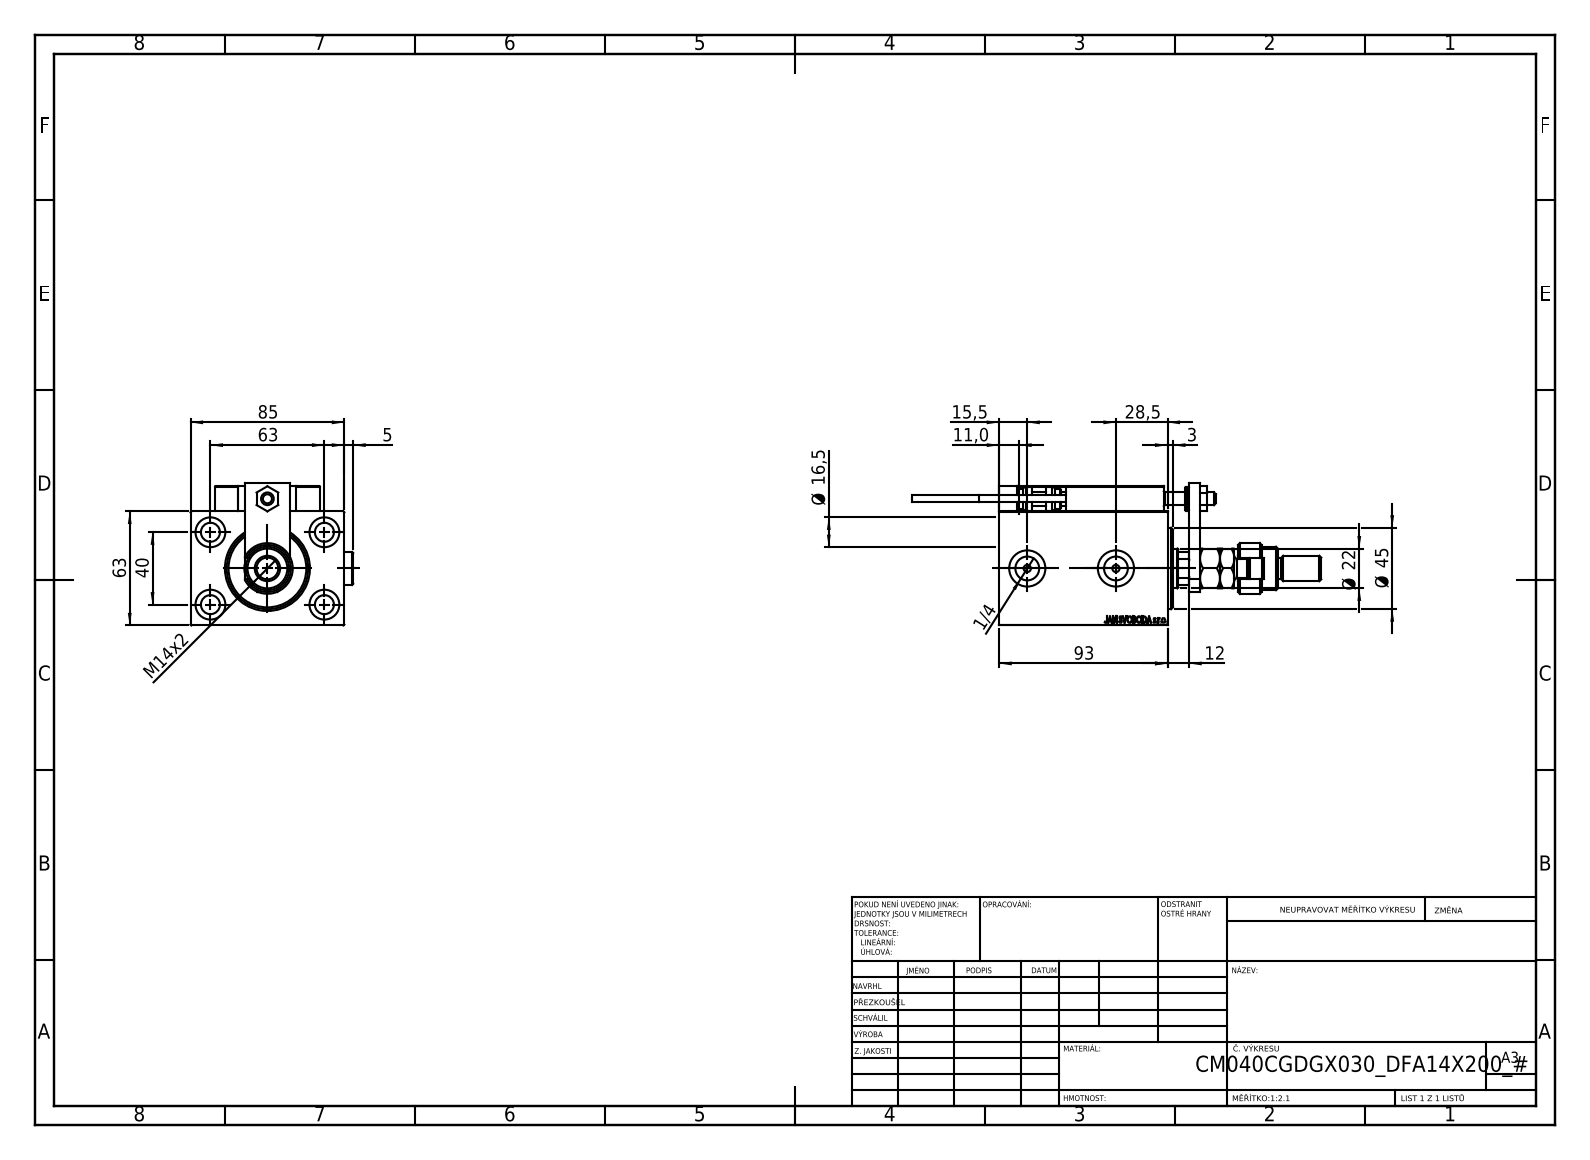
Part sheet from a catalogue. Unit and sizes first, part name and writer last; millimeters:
Units: millimetres
Overall size (bounding box): 226 × 89.9 × 78.5
Round holes (diameter × count): ⌀4 ×6, ⌀8 ×5, ⌀16.5 ×5, ⌀3.2 ×4, ⌀10.5 ×4, ⌀5 ×2, ⌀13.16 ×2, ⌀20 ×2, ⌀7 ×1, ⌀12.5 ×1, ⌀22 ×1, ⌀25.5 ×1
Round bosses / shafts (diameter × count): ⌀18 ×3, ⌀11 ×2, ⌀5 ×2, ⌀3.8 ×2, ⌀28 ×1, ⌀24 ×1, ⌀14 ×1, ⌀13 ×1
Partial cylindrical surfaces — rounded edges, fillets, slot ends (radius × count): R0.3 ×30, R3 ×2, R9.75 ×1, R10.5 ×1
Main face-to-face distances: 63, 12, 85, 81, 93, 14, 30, 77, 45, 18
Hole centre spacings: 37.31, 11.37, 20, 29.59, 29.69, 36.06, 36.53, 40
Volume: 498 659 mm³ · Surface area: 115 991 mm²
Bodies: 27 solids, 1421 faces (622 planar, 217 cylindrical, 582 other)
Part name (STEP PRODUCT): NUT_D12; KONCOVKA; X_Y_DFA; TYC_L79 (+7 more)
STEP written by: SolidWorks 2019 (CONFIG_CONTROL_DESIGN)
